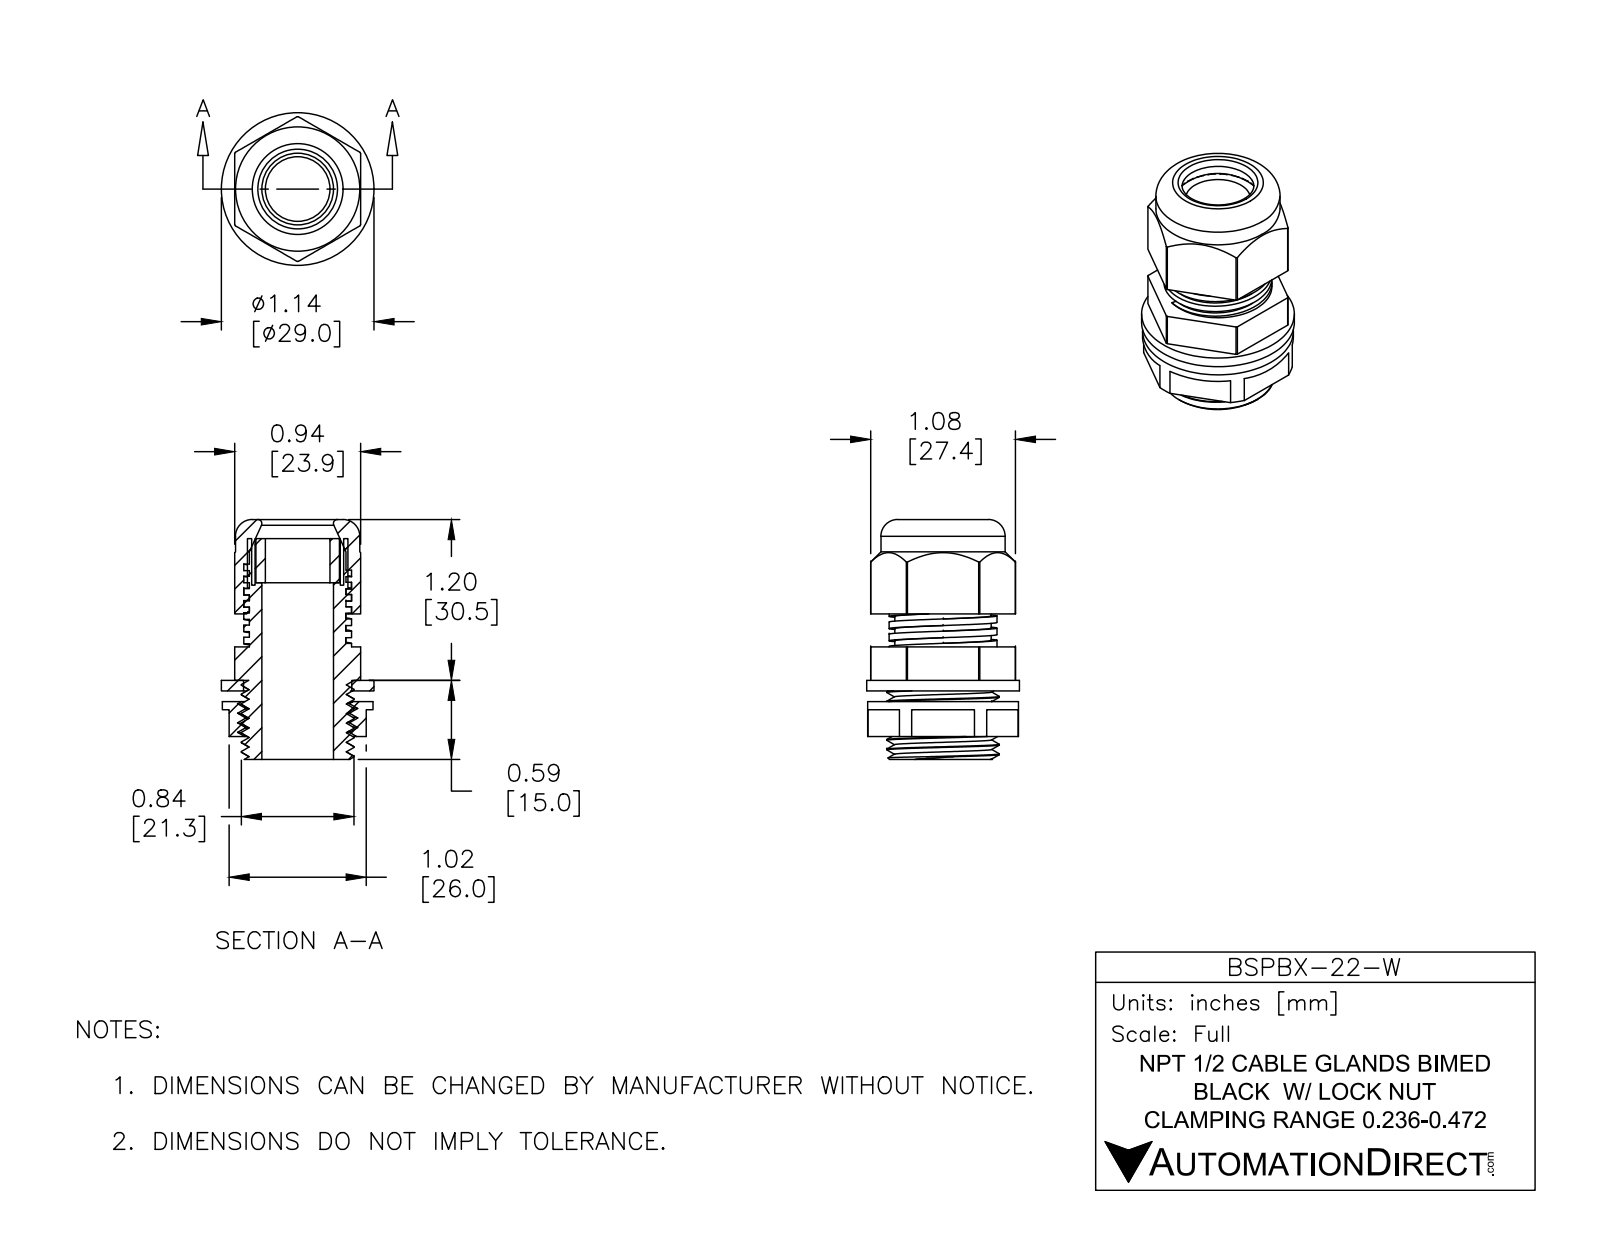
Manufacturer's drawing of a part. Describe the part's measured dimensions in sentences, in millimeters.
The part is named "BSPBX-22-W". Its 3-D file was written by "SolidWorks 2016 (AUTOMOTIVE_DESIGN)". It is 5 solids with 274 faces: 129 planar, 119 cylindrical and 26 other. Overall it measures 45.5 by 29 by 29 millimeters. Its volume is 13 700 cubic millimeters and its surface area 14 650 square millimeters. Round holes: 1 of diameter 12.2, 1 of diameter 13.6, 1 of diameter 18.3, 1 of diameter 19.9, 1 of diameter 20.5. Round bosses or shafts: 1 of diameter 29, 1 of diameter 28.6, 1 of diameter 23.5, 1 of diameter 21.3, 1 of diameter 20.4, 1 of diameter 19.1, 1 of diameter 15.8. Partial cylindrical surfaces (rounded edges, fillets, slot ends): 1 of radius 13.7. The main face-to-face distances are 23.9, 0.5, 1, 24.9, 13.2, 2, 2, 4, 13.7, 6.6.
